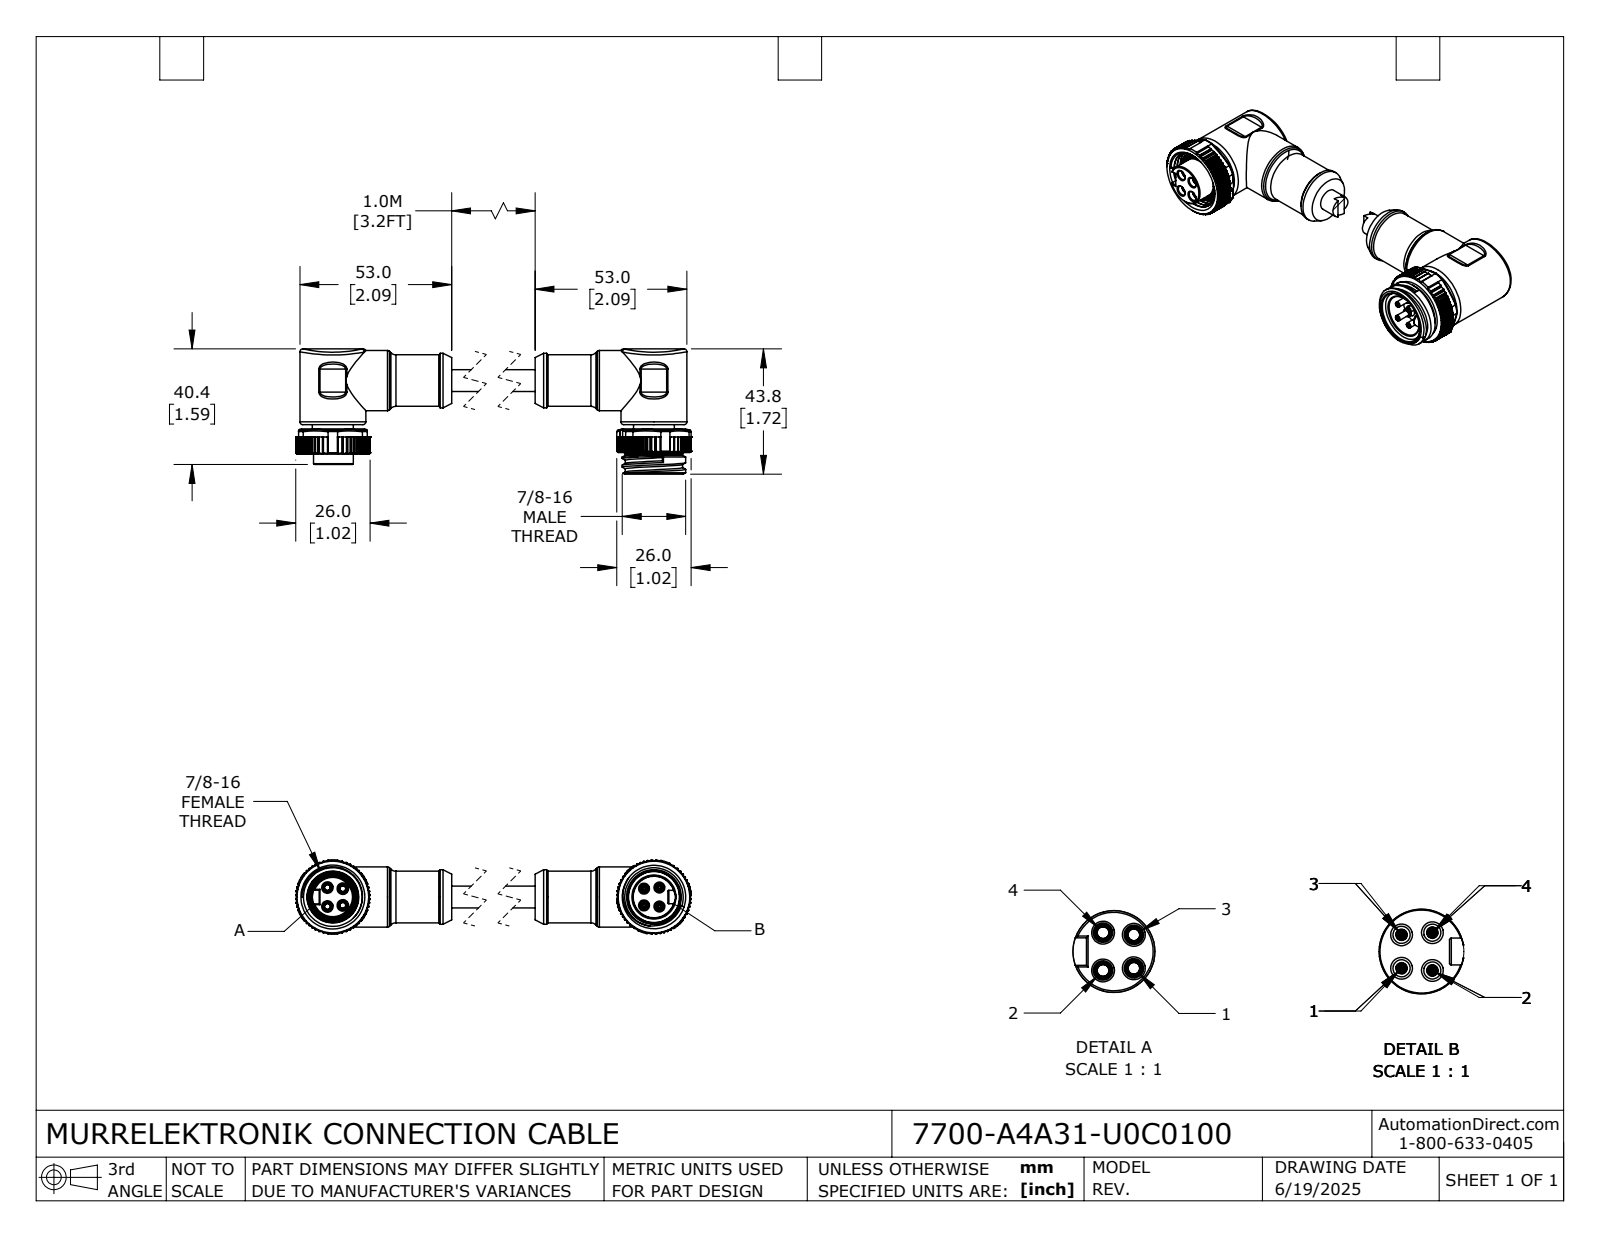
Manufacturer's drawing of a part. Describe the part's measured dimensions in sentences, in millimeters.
The part is named "7700-A4A31-U0C0100; 7700-A4A31-U0C0100_MALE; 7700-A4A31-U0C0100_FEMALE". Its 3-D file was written by "SolidWorks 2024 (CONFIG_CONTROL_DESIGN)". It is 2 solids with 1268 faces: 520 planar, 581 cylindrical and 167 other. Overall it measures 138.97 by 43.76 by 26 millimeters. Its volume is 49 781 cubic millimeters and its surface area 17 240 square millimeters. Round holes: 4 of diameter 2.05, 4 of diameter 3, 4 of diameter 3.4, 2 of diameter 15.6, 1 of diameter 15.5, 1 of diameter 18.5, 1 of diameter 20.5, 1 of diameter 22.22. Round bosses or shafts: 4 of diameter 3, 4 of diameter 2, 2 of diameter 23, 2 of diameter 18.1, 2 of diameter 17.8, 2 of diameter 14.3, 1 of diameter 22.17, 1 of diameter 21. Partial cylindrical surfaces (rounded edges, fillets, slot ends): 252 of radius 0.2, 34 of radius 0.3, 8 of radius 0.1, 8 of radius 1, 4 of radius 0.7, 4 of radius 0.73, 4 of radius 2.5, 2 of radius 13. The main face-to-face distances are 1.5, 8.8, 7.3, 9.7, 0.9, 7, 30, 8.2, 21, 4.2. The hole center spacings are 3.81, 4.54, 5.39, 8.22, 109.56, 114.95, 5.84, 6.6.
